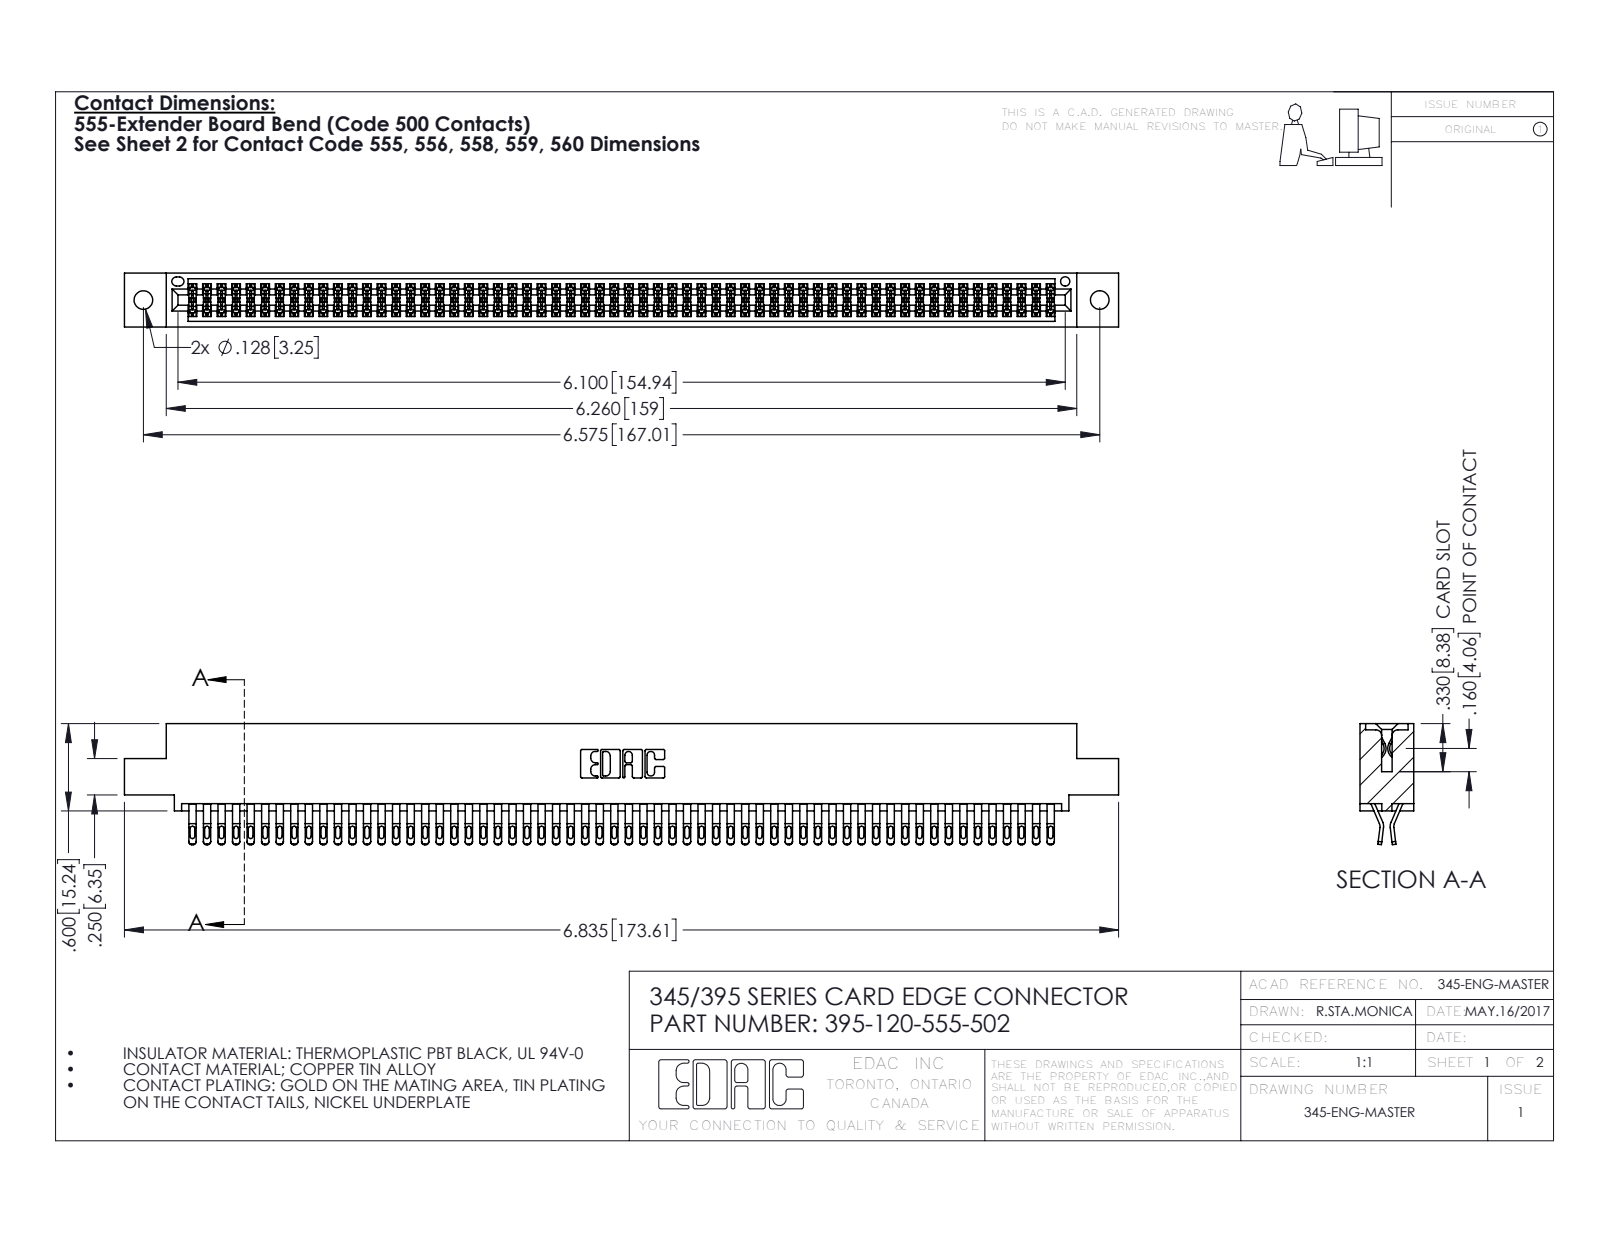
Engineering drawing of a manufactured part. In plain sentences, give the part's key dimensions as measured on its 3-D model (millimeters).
The part is named "395-120-555-502; 345-292-001_555 Tail; 345 Part_0.110 Offset - 0.128 Dia". Its 3-D file was written by "SolidWorks 2016 (CONFIG_CONTROL_DESIGN)". It is 121 solids with 6850 faces: 3804 planar, 3046 cylindrical and 0 other. Overall it measures 173.6 by 21.1 by 9.4 millimeters. Its volume is 17 270 cubic millimeters and its surface area 26 910 square millimeters. Round holes: 2 of diameter 3.3, 1 of diameter 1.6. Partial cylindrical surfaces (rounded edges, fillets, slot ends): 300 of radius 0.4, 240 of radius 0.5, 180 of radius 0.2, 22 of radius 0.3, 6 of radius 0.2, 6 of radius 0.8, 3 of radius 0.7, 2 of radius 0.3. The main face-to-face distances are 7.6, 1.8, 0.6, 9.4, 5.1, 2.5, 6.9, 5.7, 4.4, 3.8. The hole center spacings are 6.9, 161, 167.
